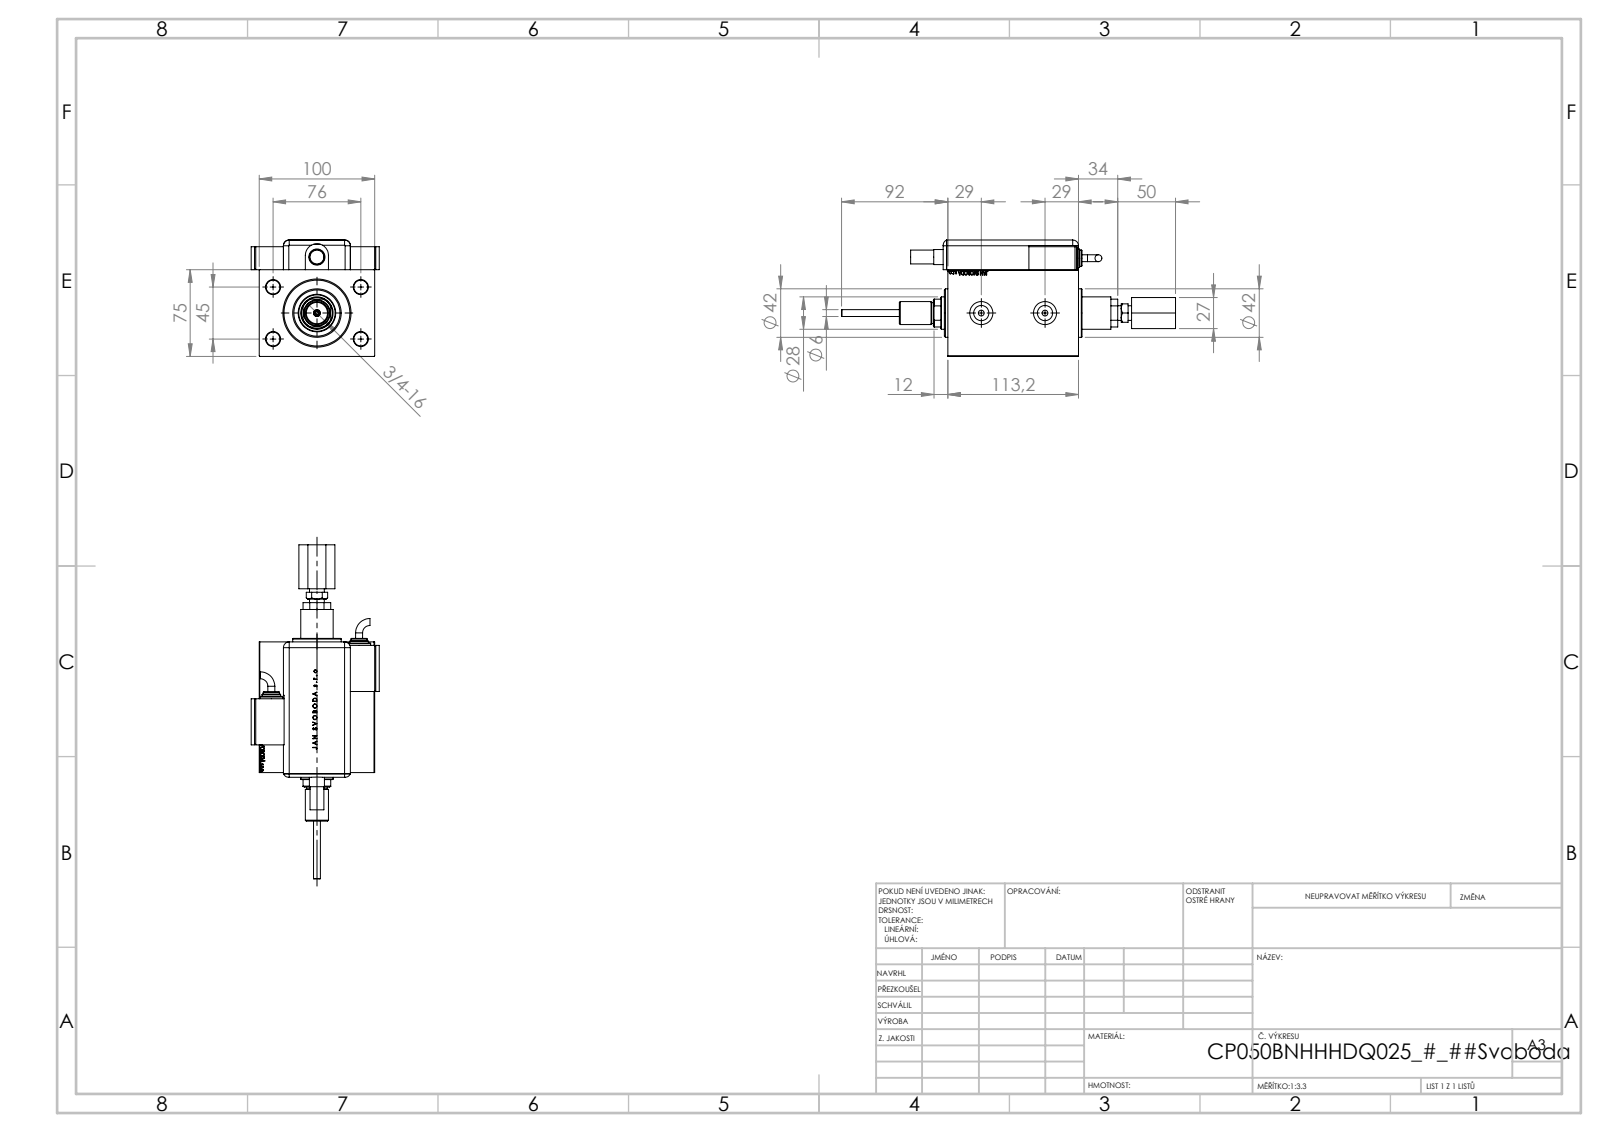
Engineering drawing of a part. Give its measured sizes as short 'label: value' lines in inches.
name: V450CP_MALE_METRIC; SWITCH_Q_FRONT_BACK; V450DCP_VC_B; KRYT (+6 more)
written by: SolidWorks 2019 (CONFIG_CONTROL_DESIGN)
unit: in
bodies: 11 solids, 1322 faces (618 planar, 141 cylindrical, 563 other)
size: 11.386 × 4.37 × 3.969
volume: 59.93 in³; area: 283.2 in²
holes: 4× ⌀0.157, 4× ⌀0.472, 2× ⌀0.197, 2× ⌀0.315, 2× ⌀0.383, 2× ⌀0.518, 2× ⌀0.591, 2× ⌀0.787, 1× ⌀0.118, 1× ⌀0.236, 1× ⌀0.551, 1× ⌀0.728
bosses: 3× ⌀0.787, 2× ⌀0.63, 2× ⌀0.551, 2× ⌀0.236, 1× ⌀1.654, 1× ⌀0.709, 1× ⌀0.512, 1× ⌀0.503
rounds: 9× R0.197, 1× R0.394, 1× R0.531
face distances: 0.118, 2.953, 3.937, 4.457, 0.039, 0.551, 3.969, 1.016, 0.945, 3.906
hole spacings: 1.739, 1.772, 1.813, 2.992, 3.17, 3.477, 0.787, 0.804
